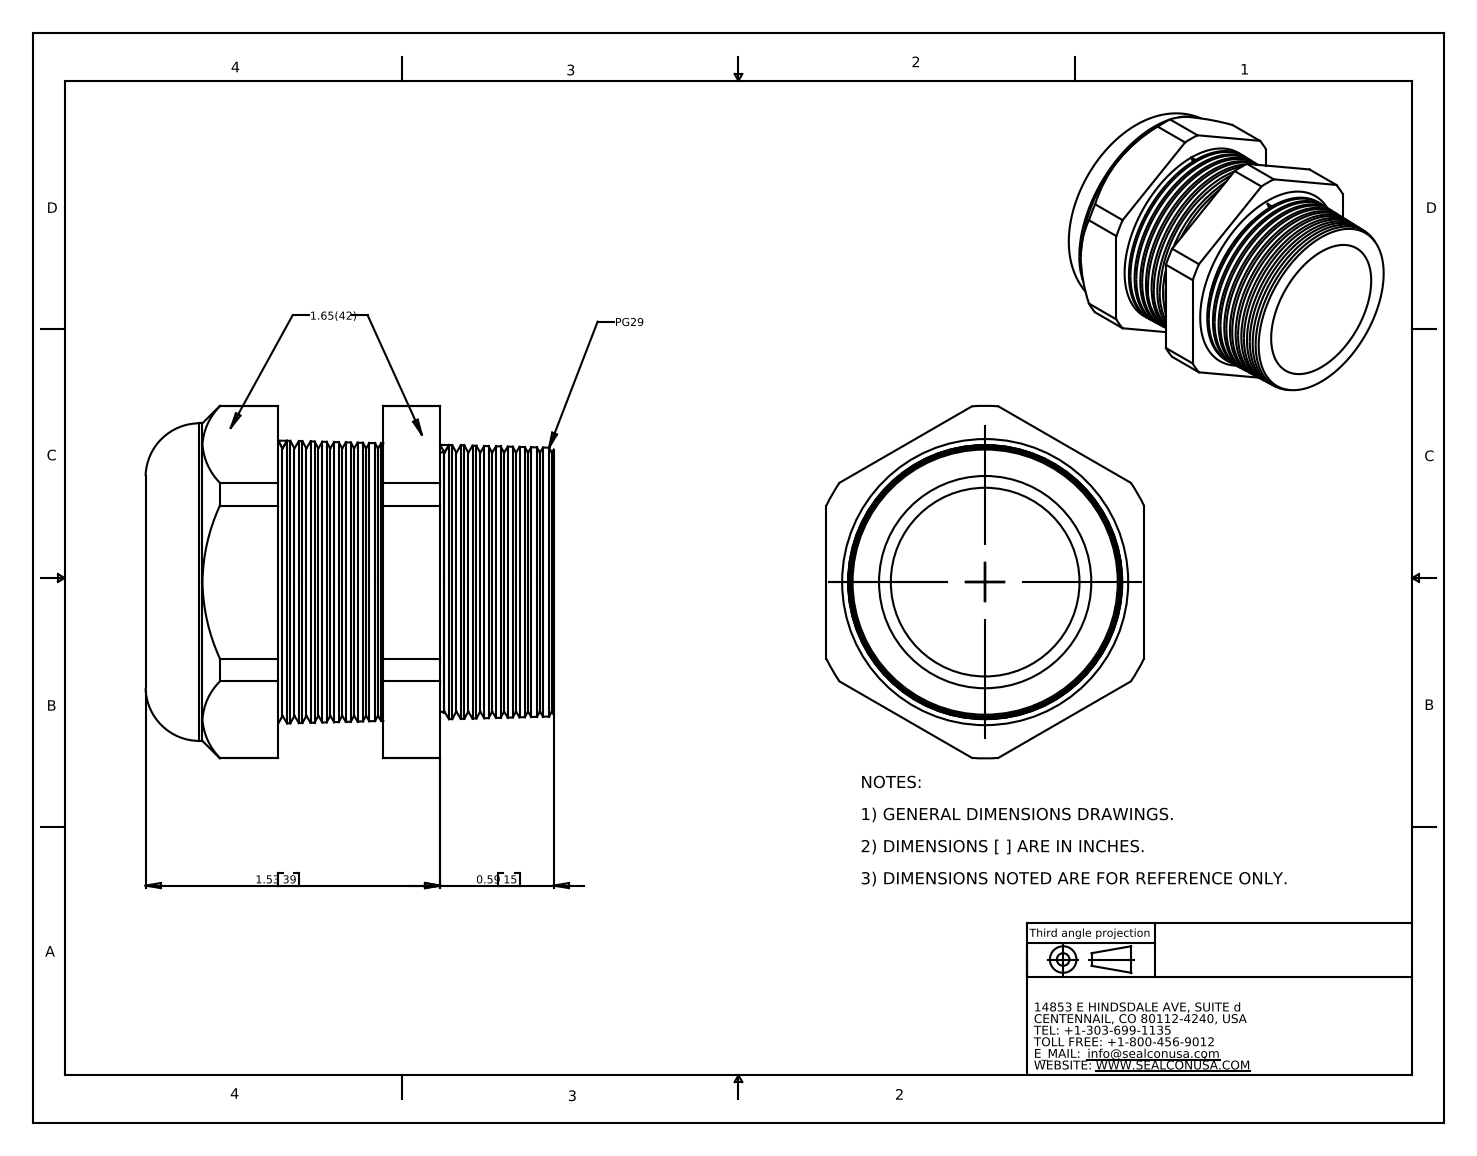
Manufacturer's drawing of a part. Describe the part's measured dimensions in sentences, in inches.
The part is named "CD29CA-BK". Its 3-D file was written by "SolidWorks 2007 (CONFIG_CONTROL_DESIGN)". It is 2 solids with 169 faces: 19 planar, 22 cylindrical and 128 other. Overall it measures 2.12 by 1.831 by 1.65 inches. Its volume is 2.179 cubic inches and its surface area 26.32 square inches. Round holes: 1 of diameter 0.98, 1 of diameter 1.103. Round bosses or shafts: 1 of diameter 1.65. Partial cylindrical surfaces (rounded edges, fillets, slot ends): 1 of radius 0.916. The main face-to-face distances are 1.65, 0.546, 0.841, 0.295, 1.431, 0.885, 0.59, 1.65, 0.394, 0.94.
